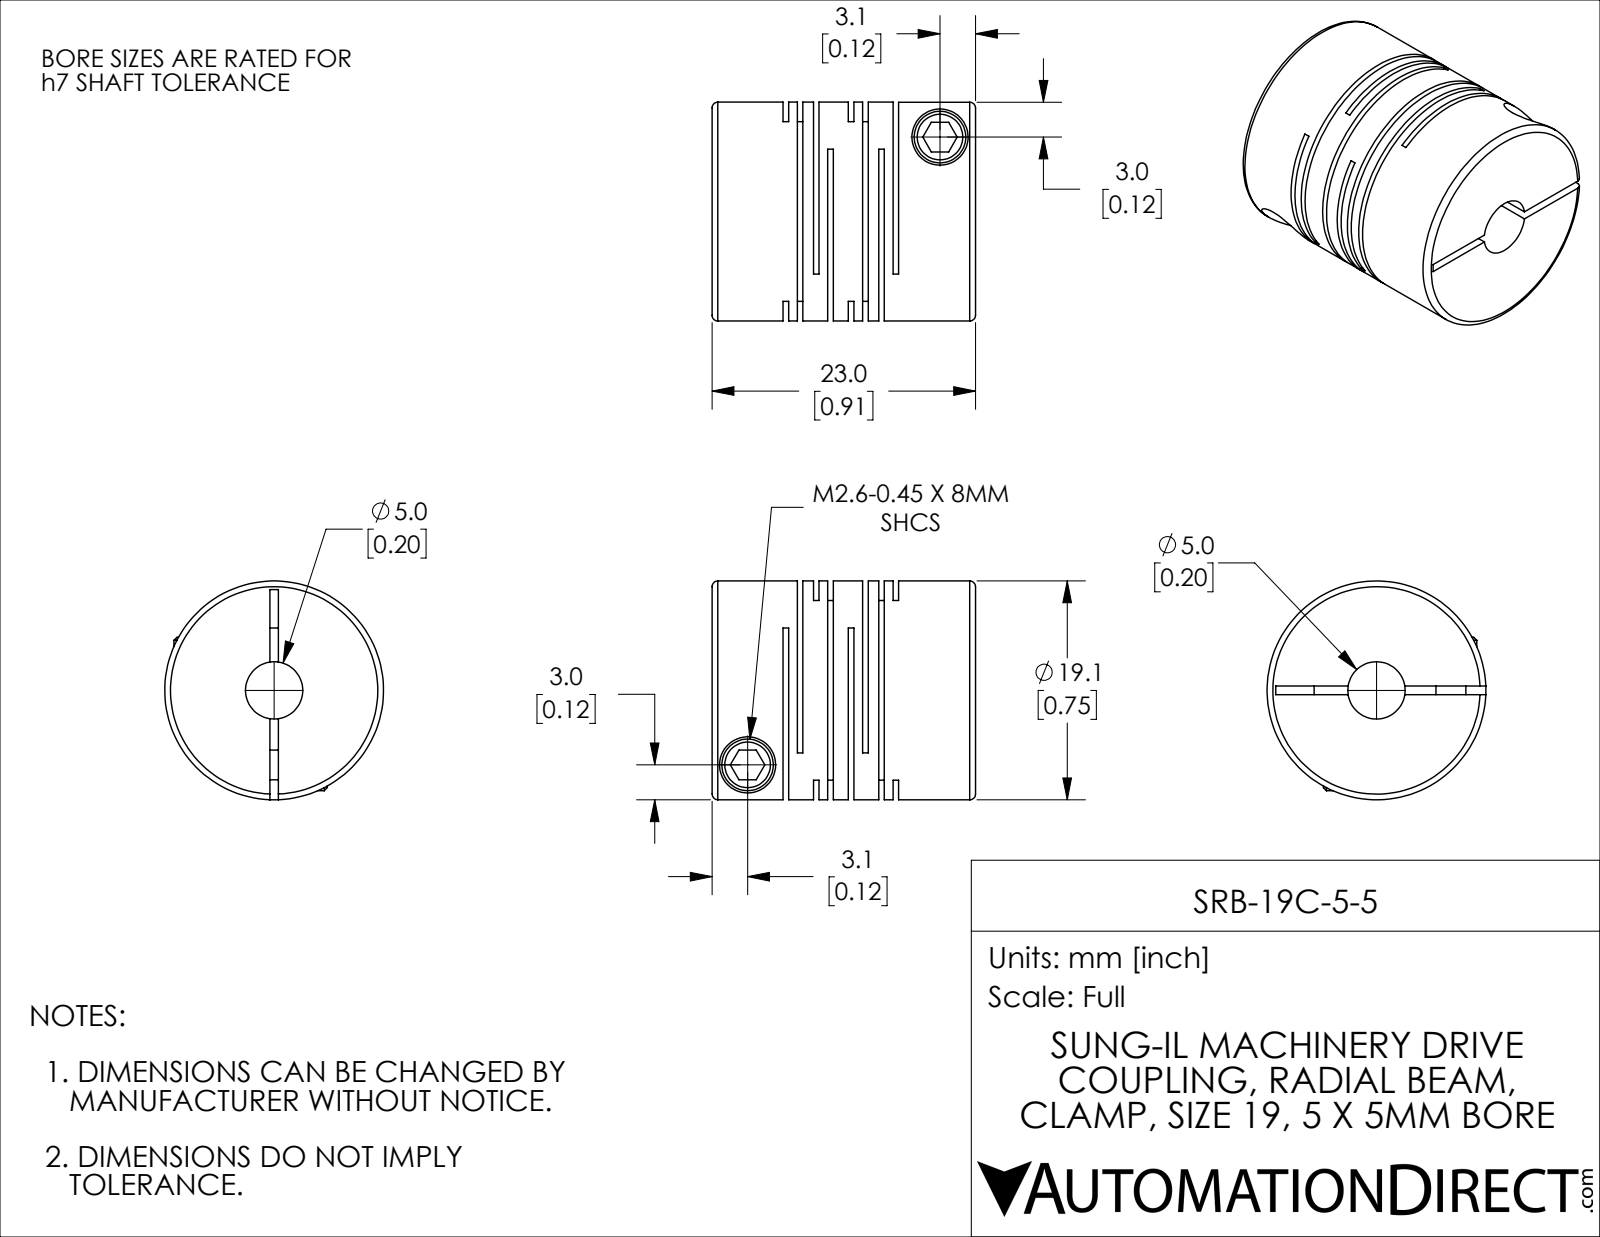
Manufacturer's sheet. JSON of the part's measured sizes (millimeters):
{"part_name": "SRB-19C-5-5", "step_written_by": "SolidWorks 2021 (CONFIG_CONTROL_DESIGN)", "units": "millimeters", "bodies": {"solids": 1, "faces": 114, "planar": 60, "cylindrical": 42, "other": 12}, "overall_size": [23, 19.1, 19.1], "volume_mm3": 5036, "surface_area_mm2": 6133, "round_holes": [[2.6, 2], [4.9, 2], [5, 1]], "round_bosses_or_shafts": [[4.5, 2], [19.1, 1]], "face_to_face_distances": [5.7, 0.48, 1.25, 2.65, 2.17, 3.05, 5.22, 4.45, 0.77, 1.4]}
